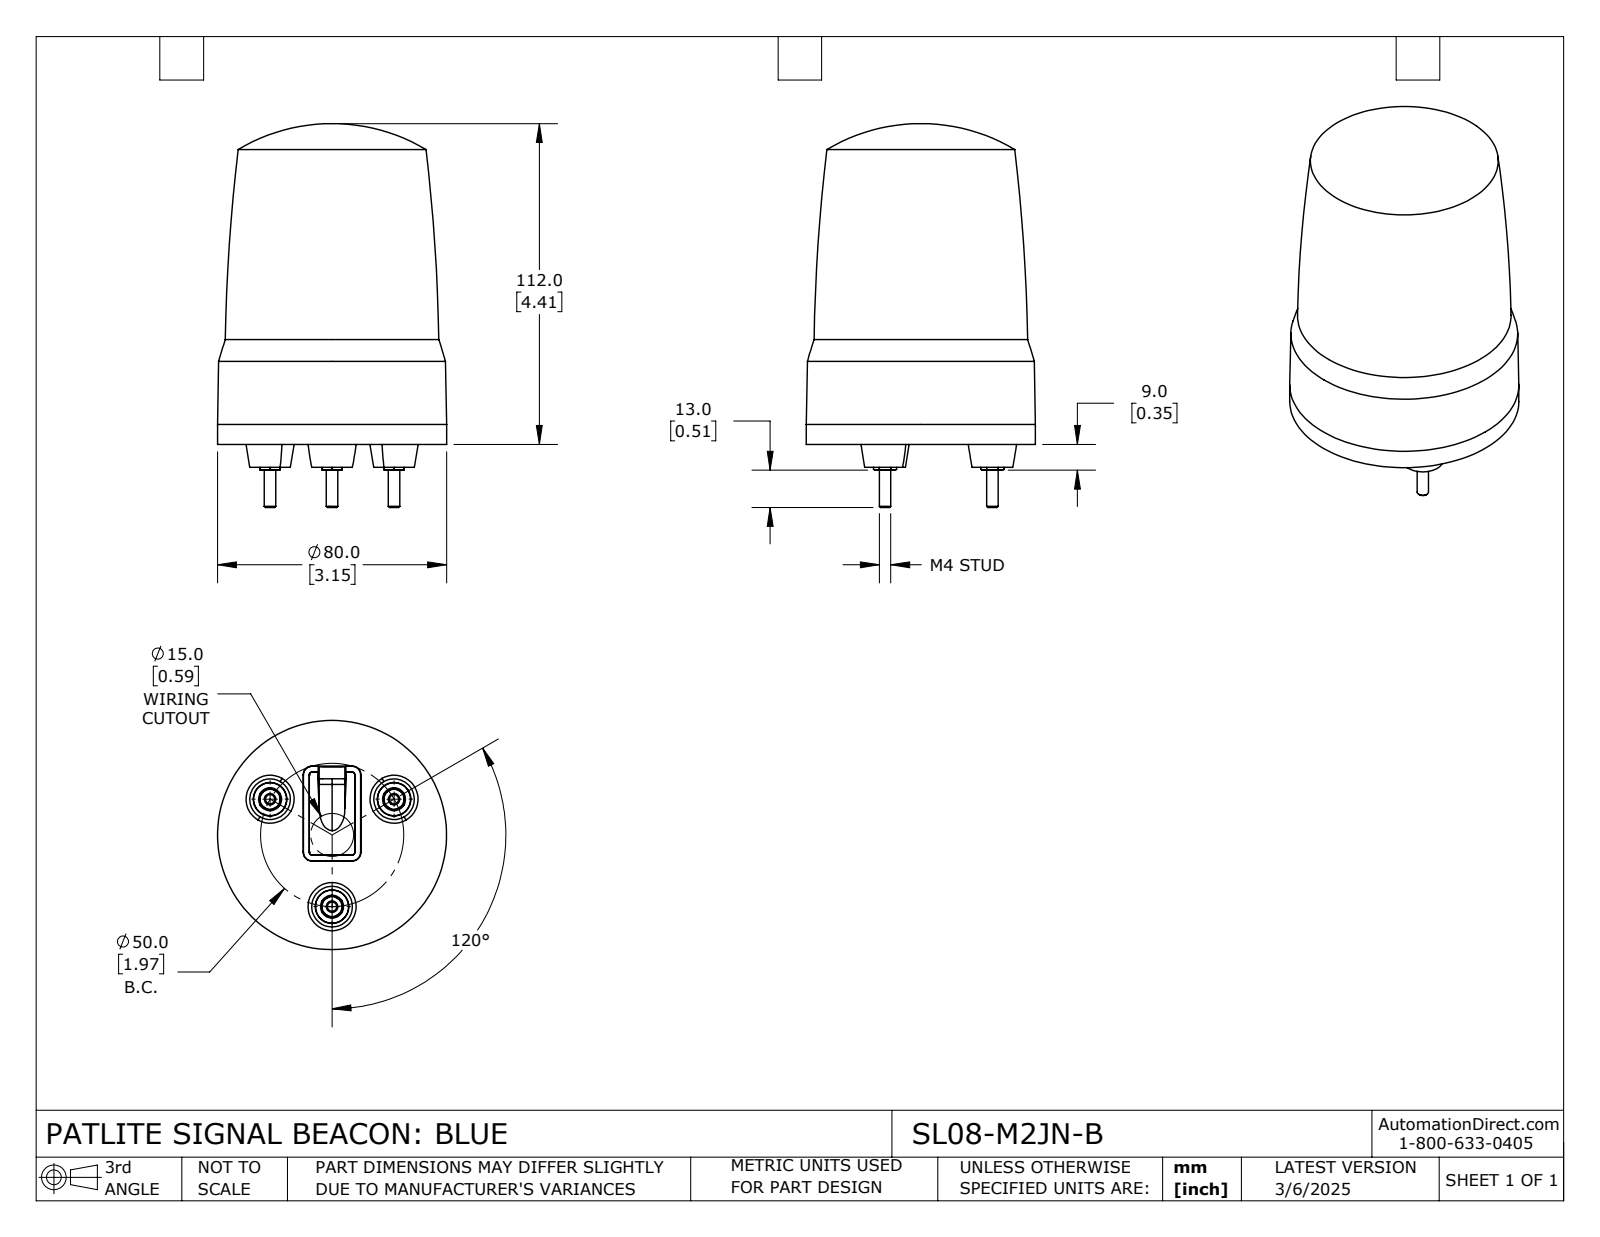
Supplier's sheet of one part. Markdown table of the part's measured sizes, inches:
| quantity | value |
| --- | --- |
| part name | SL08-M2JN-B |
| STEP written by | SolidWorks 2024 (CONFIG_CONTROL_DESIGN) |
| units | inches |
| bodies | 1 solid, 138 faces (47 planar, 14 cylindrical, 77 other) |
| overall size | 5.276 × 3.15 × 3.15 |
| volume | 28.27 in³ |
| surface area | 54.88 in² |
| round bosses / shafts (diameter × count) | 0.315 × 3, 0.157 × 3, 3.15 × 1 |
| main face-to-face distances | 0.033, 0.096, 0.063, 0.209, 0.242, 0.305, 0.106, 0.315, 0.348, 0.411 |
